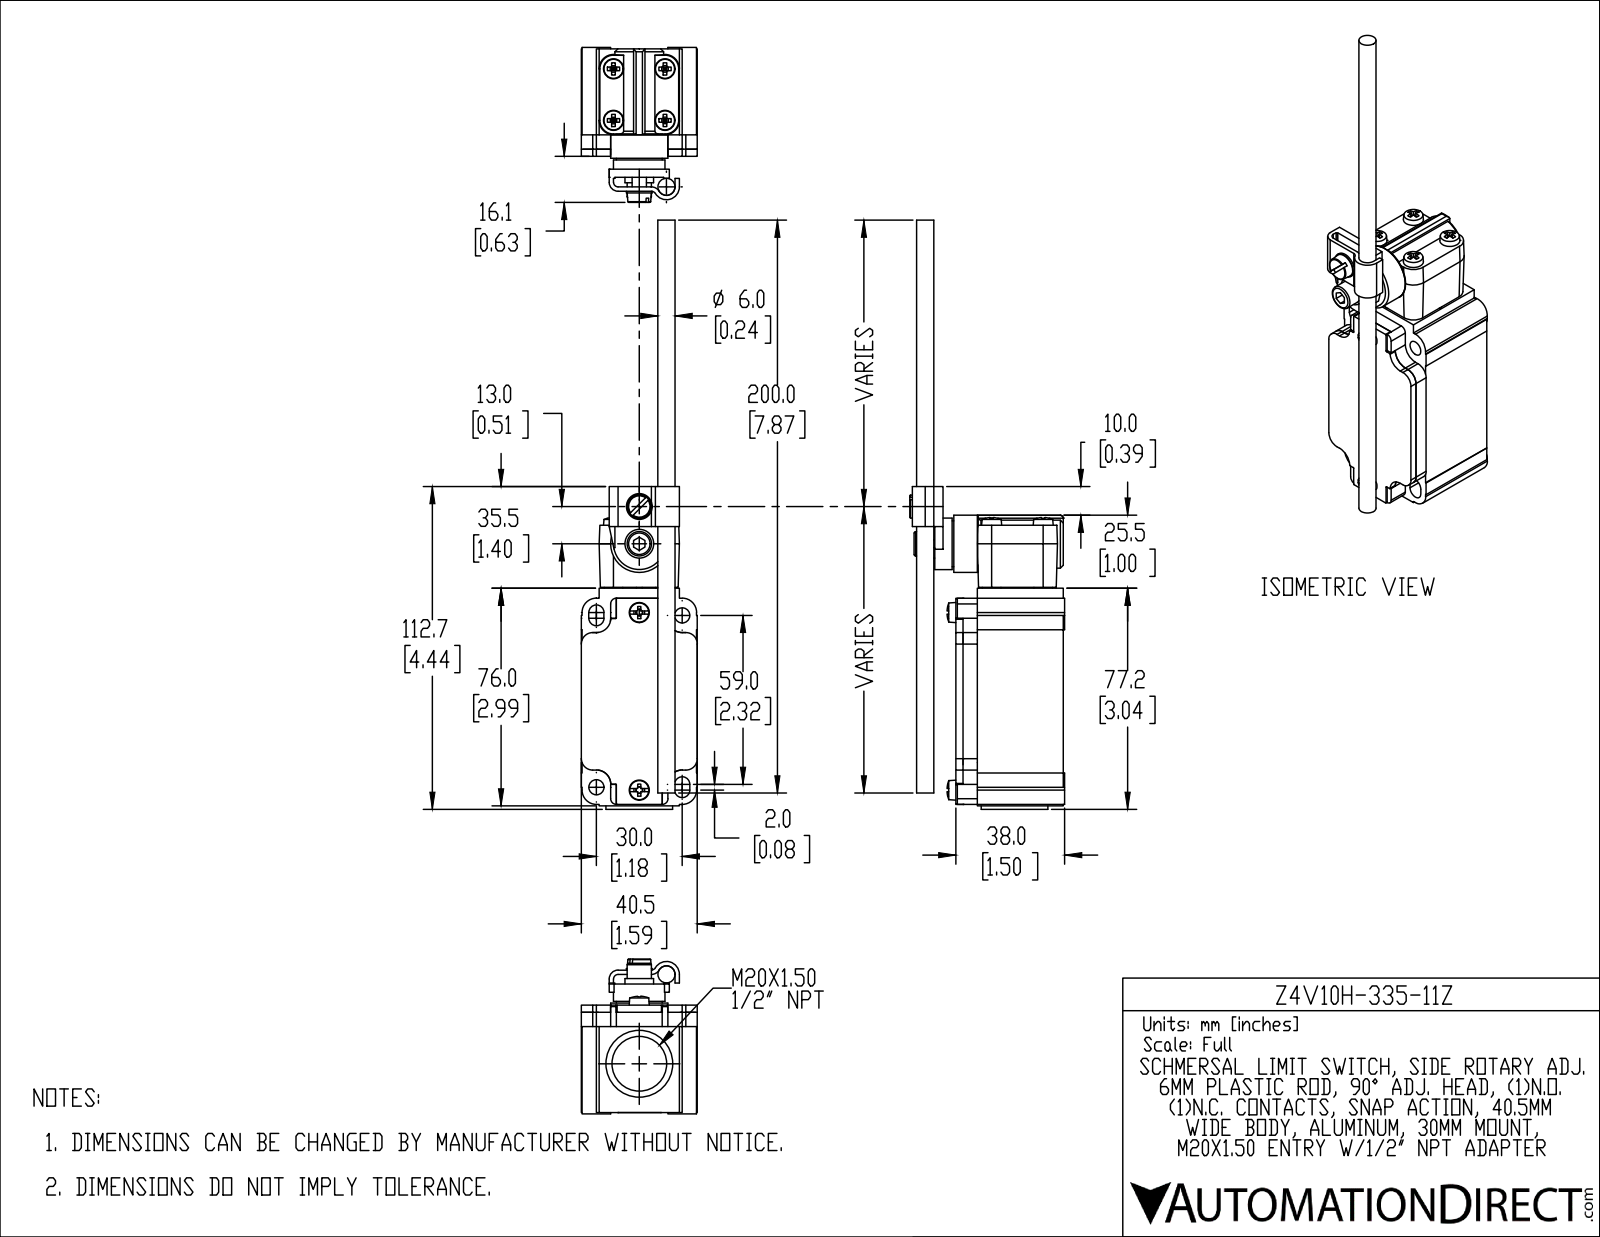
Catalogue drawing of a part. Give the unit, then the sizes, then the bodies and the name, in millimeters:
Units: millimetres
Overall size (bounding box): 205.7 × 54.1 × 40.5
Round holes (diameter × count): ⌀2.05 ×4, ⌀3.8 ×4, ⌀5.3 ×2, ⌀14 ×1, ⌀15 ×1, ⌀16.5 ×1, ⌀18.05 ×1, ⌀19.06 ×1
Round bosses / shafts (diameter × count): ⌀18 ×2, ⌀2 ×2, ⌀23.3 ×1, ⌀20 ×1, ⌀17 ×1, ⌀16 ×1, ⌀10 ×1, ⌀9 ×1
Partial cylindrical surfaces — rounded edges, fillets, slot ends (radius × count): R0.25 ×12, R4 ×12, R5 ×12, R2 ×4, R2.65 ×4, R3.25 ×4, R5 ×4, R1 ×2
Main face-to-face distances: 0.5, 35.5, 2, 2.5, 35, 37.5, 30, 5, 40.5, 5.5
Hole centre spacings: 9.66, 23.31, 12.5, 12.73, 17.68, 18, 12.04, 12.54
Volume: 129 096 mm³ · Surface area: 34 316 mm²
Bodies: 1 solid, 730 faces (531 planar, 136 cylindrical, 63 other)
Part name (STEP PRODUCT): Z4V10H_335-11Z
STEP written by: CREO PARAMETRIC BY PTC INC, 2019030 (CONFIG_CONTROL_DESIGN)
